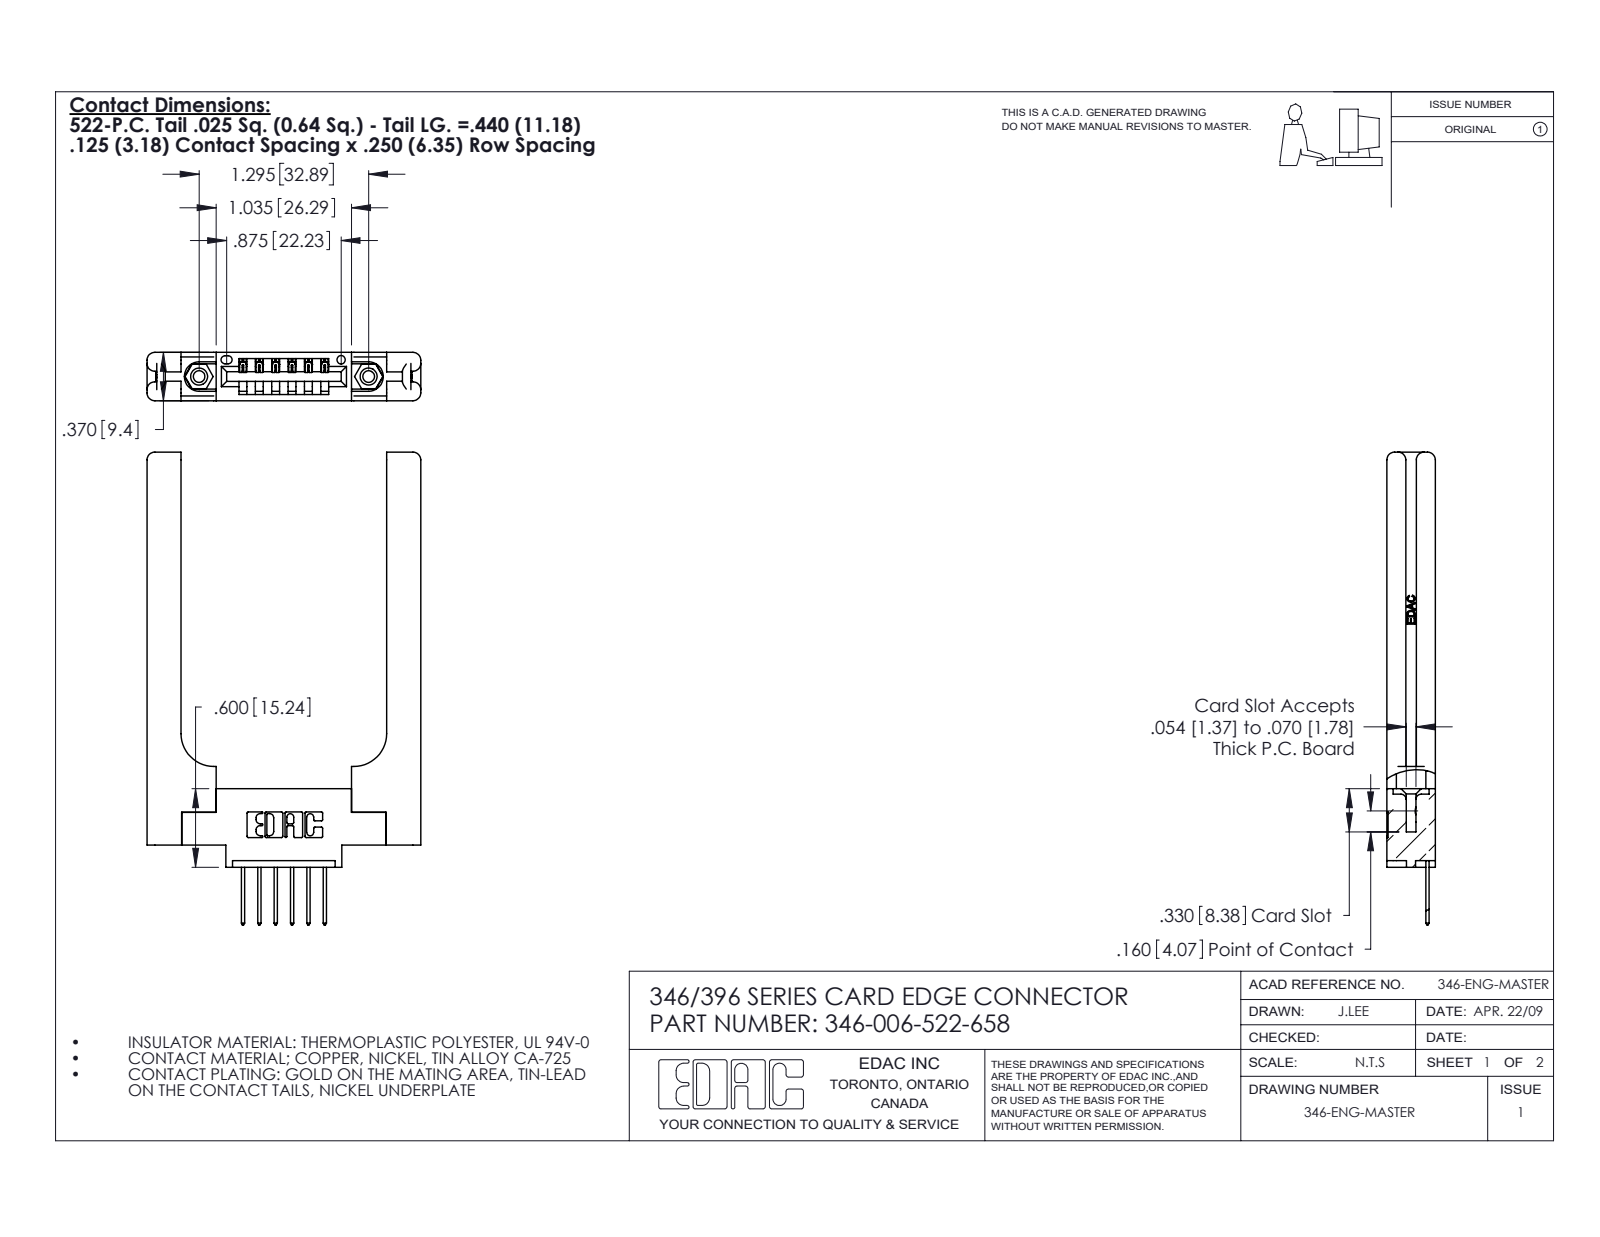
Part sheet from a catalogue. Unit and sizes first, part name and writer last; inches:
Units: inches
Overall size (bounding box): 3.61 × 2.091 × 0.37
Round holes (diameter × count): ⌀0.089 ×2, ⌀0.125 ×2, ⌀0.156 ×2, ⌀0.064 ×1
Round bosses / shafts (diameter × count): ⌀0.155 ×2
Partial cylindrical surfaces — rounded edges, fillets, slot ends (radius × count): R0.01 ×22, R0.06 ×16, R0.006 ×12, R0.01 ×12, R0.007 ×6, R0.031 ×6, R0.026 ×3, R0.03 ×2
Main face-to-face distances: 0.37, 0.15, 0.22, 0.072, 0.148, 0.25, 1.571, 0.048, 0.322, 0.102
Hole centre spacings: 0.246, 1.092, 1.295
Volume: 0.743 in³ · Surface area: 16.78 in²
Bodies: 11 solids, 744 faces (482 planar, 202 cylindrical, 60 other)
Part name (STEP PRODUCT): 346-006-522-658; 345-292-001_345-293-122; 346-220-058_345-220-058; 345-250-001_345-250-001-102 (+1 more)
STEP written by: SolidWorks 2020 (CONFIG_CONTROL_DESIGN)
